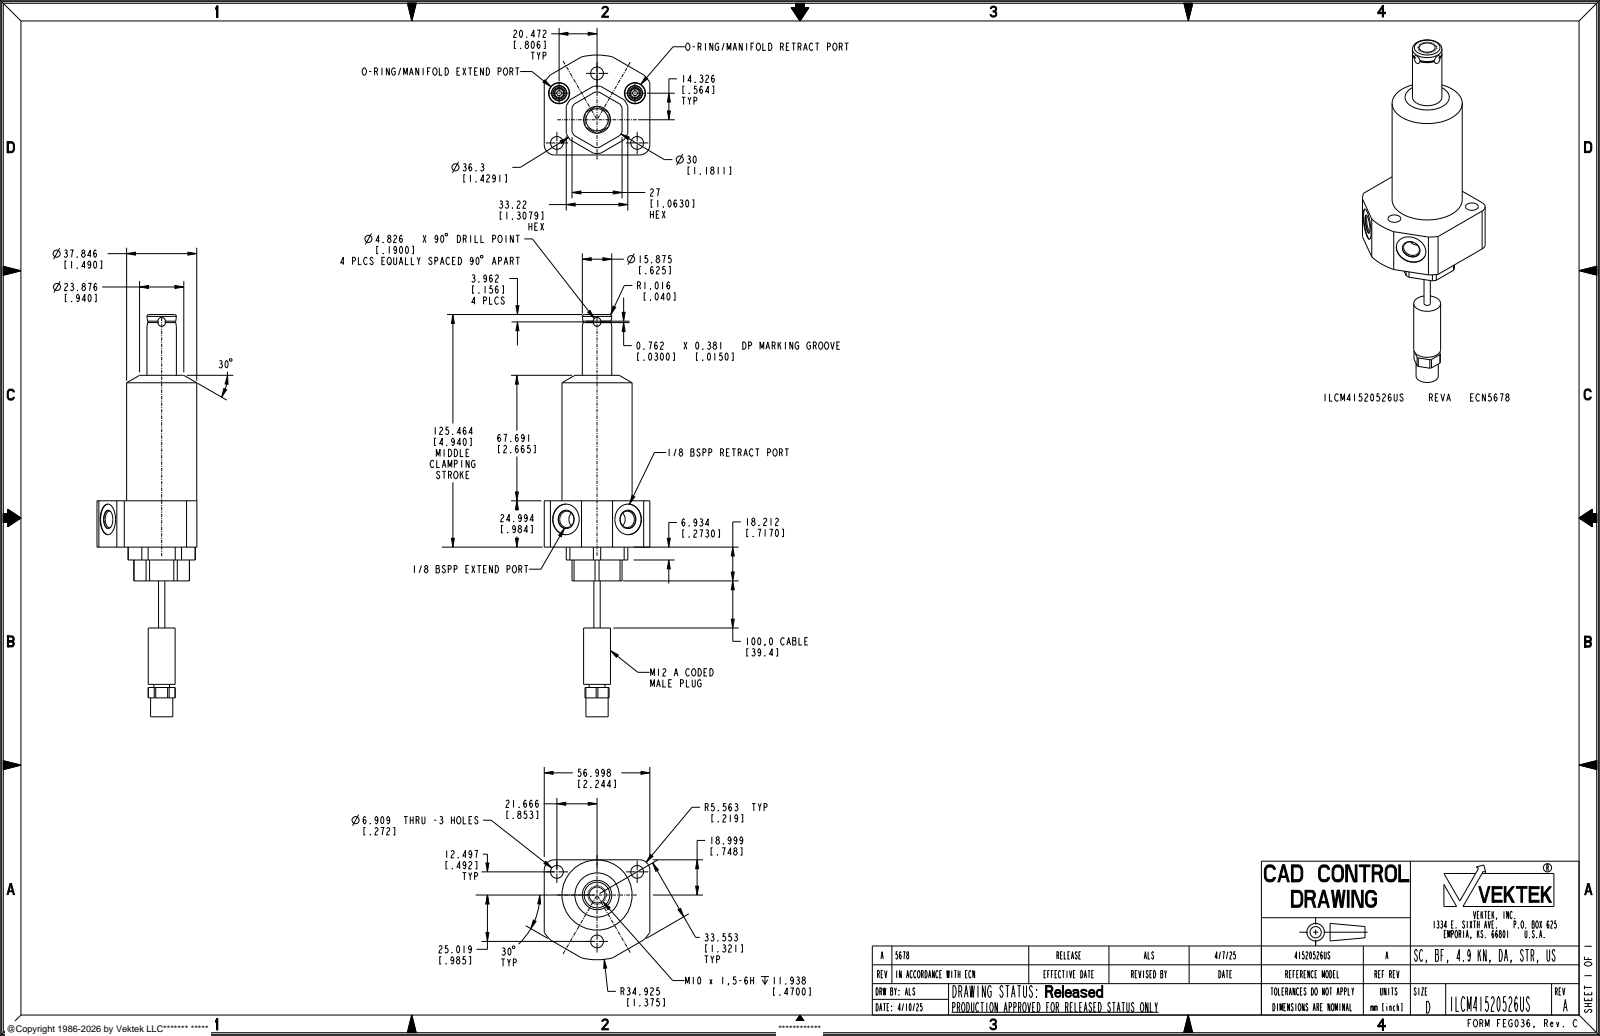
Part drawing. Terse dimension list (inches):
name: ILCM41520526US
written by: CREO PARAMETRIC BY PTC INC, 2021164 (AUTOMOTIVE_DESIGN)
unit: in
bodies: 1 solid, 184 faces (75 planar, 79 cylindrical, 30 other)
size: 8.543 × 2.753 × 2.559
volume: 10.12 in³; area: 43.47 in²
holes: 3× ⌀0.272, 2× ⌀0.098, 2× ⌀0.256, 2× ⌀0.348, 2× ⌀0.39, 2× ⌀0.449, 2× ⌀0.65, 1× ⌀0.339
bosses: 2× ⌀0.216, 1× ⌀1.49, 1× ⌀0.625, 1× ⌀0.571, 1× ⌀0.472, 1× ⌀0.394, 1× ⌀0.335, 1× ⌀0.134
rounds: 2× R0.219, 1× R0.298, 1× R0.591, 1× R0.715, 1× R1.375
face distances: 0.984, 2.244, 0.717, 1.701, 0.122, 1.185, 1.063, 0.444, 0.273, 1.257
hole spacings: 0.985, 0.909, 0.984, 1.057, 1.706, 1.967, 1.612, 1.706
